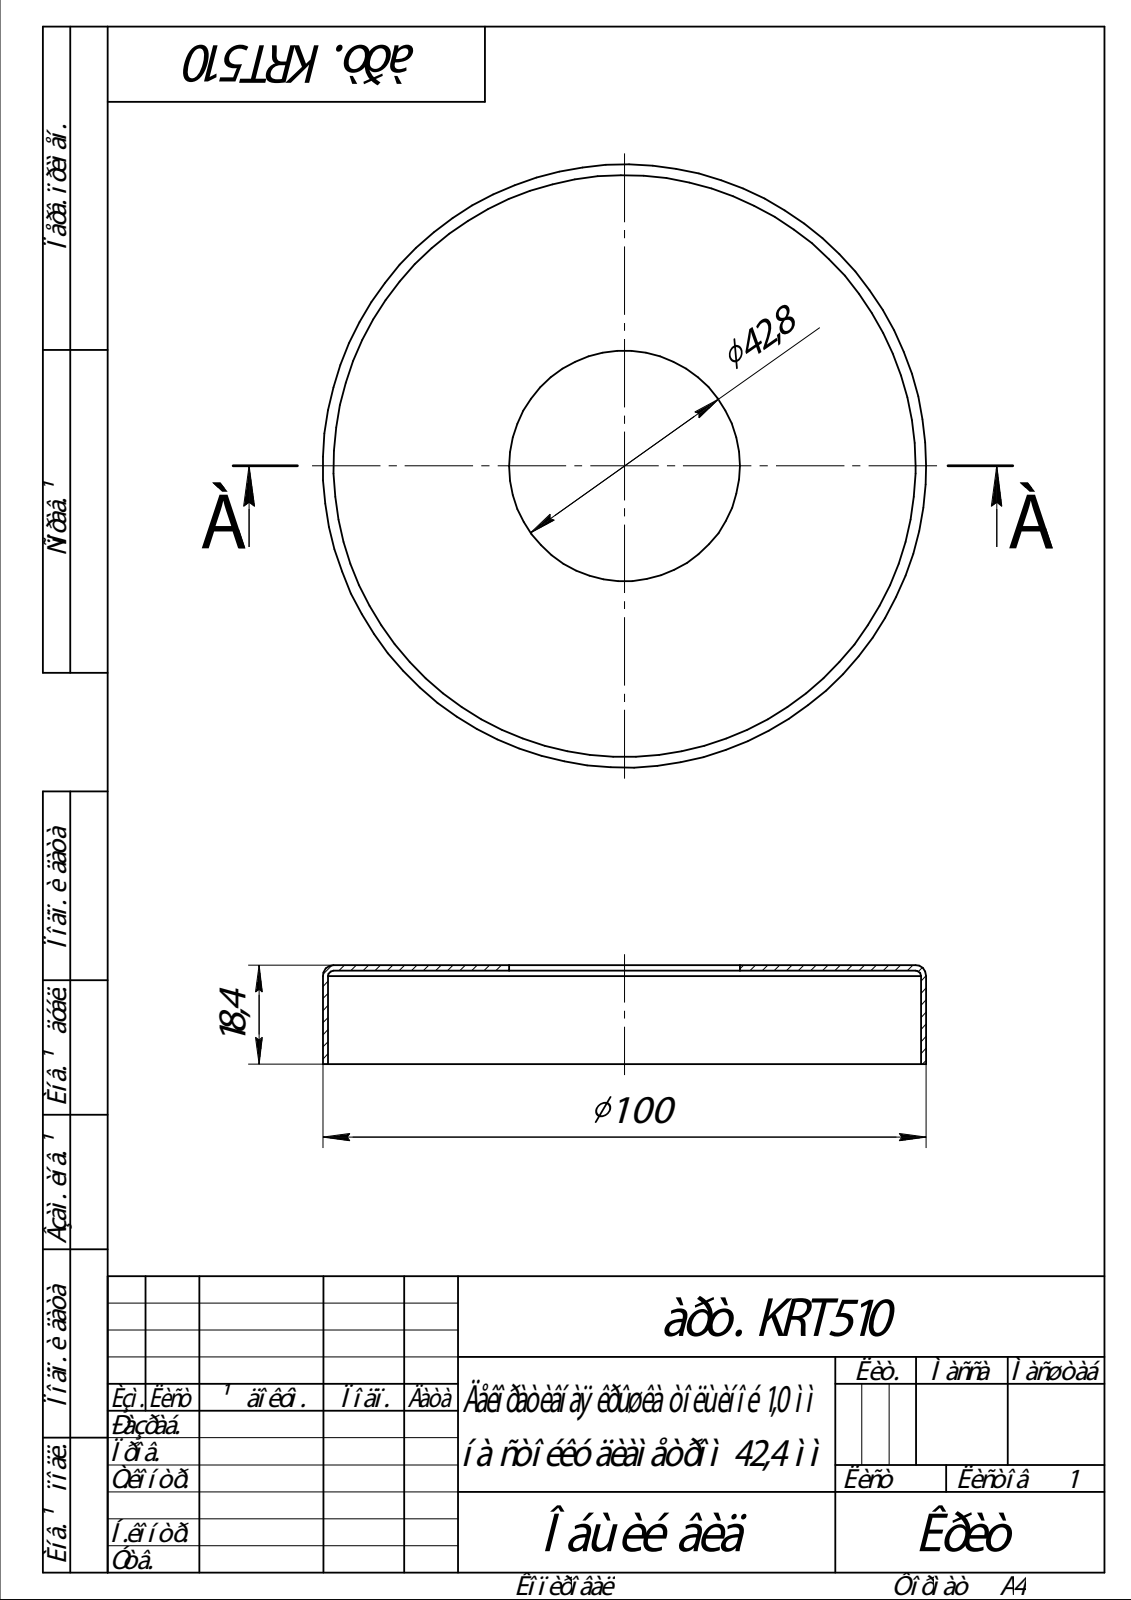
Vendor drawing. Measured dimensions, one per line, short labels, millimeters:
name: арт. KRT510
written by: SolidWorks 2014 (AUTOMOTIVE_DESIGN)
unit: mm
bodies: 1 solid, 13 faces (3 planar, 6 cylindrical, 4 other)
size: 112 × 112 × 18.4
volume: 14 255 mm³; area: 28 996 mm²
holes: 1× ⌀42.8, 1× ⌀110
bosses: 1× ⌀112
face distances: 1, 17.4, 18.4
